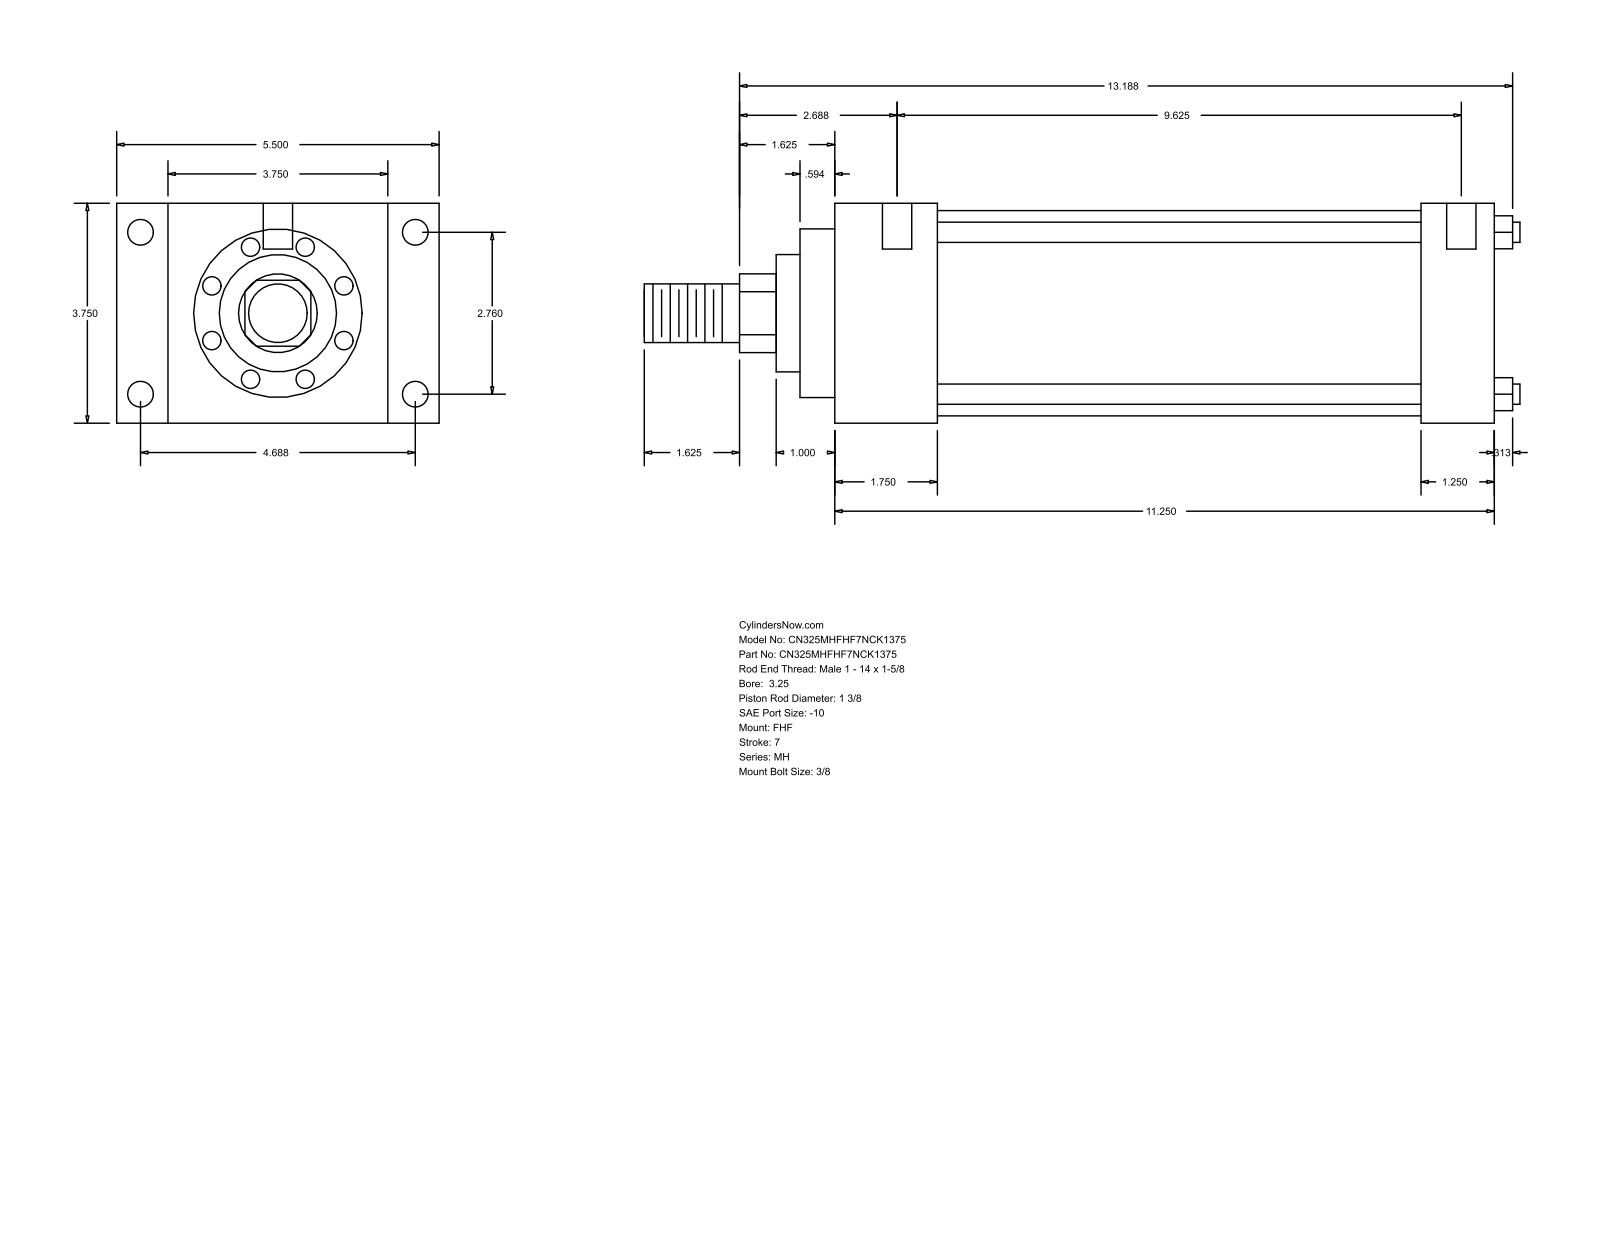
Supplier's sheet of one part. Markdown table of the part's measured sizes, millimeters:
| quantity | value |
| --- | --- |
| part name | MH_FHF__0325_1.375 |
| STEP written by | GSSL Pune (CONFIG_CONTROL_DESIGN) |
| units | millimeters |
| bodies | 0 solids, 90 faces (61 planar, 29 cylindrical, 0 other) |
| overall size | 379.41 × 139.7 × 95.25 |
| round holes (diameter × count) | 5.56 × 4, 11.13 × 4, 12.7 × 2 |
| round bosses / shafts (diameter × count) | 8.76 × 4, 88.9 × 1, 73.03 × 1, 50.8 × 1, 34.92 × 1, 25.4 × 1 |
| partial cylindrical surfaces (radius × count) | 17.06 × 1 |
| main face-to-face distances | 95.24, 285.75, 44.45, 241.3, 22.23, 117.47, 139.7, 254, 209.55, 31.75 |
| hole center spacings | 70.1, 119.06, 138.16, 250.83, 1.59, 4.76, 244.48, 246.07 |
